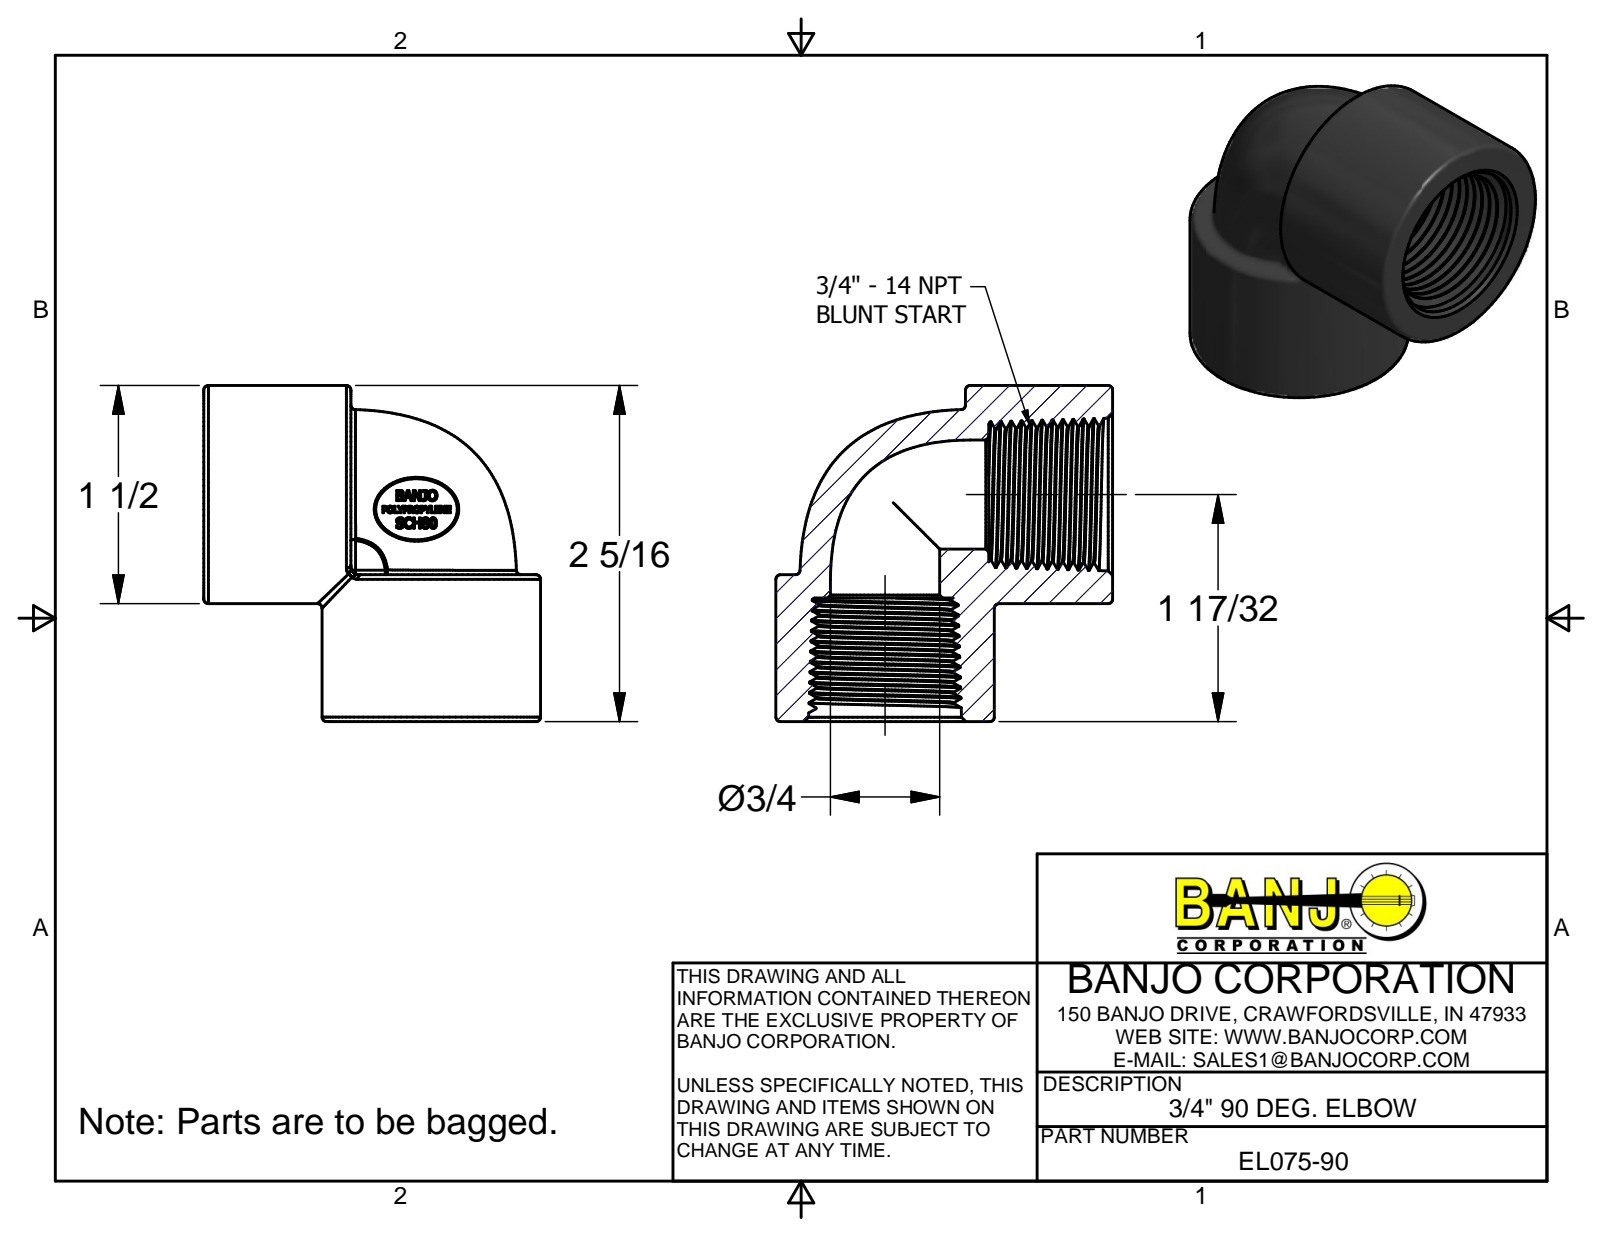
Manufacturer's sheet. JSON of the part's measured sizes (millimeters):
{"part_name": "EL075-90", "step_written_by": "Autodesk Inventor 2014 (AUTOMOTIVE_DESIGN)", "units": "millimeters", "bodies": {"solids": 2, "faces": 449, "planar": 173, "cylindrical": 11, "other": 265}, "overall_size": [58.73, 58.7, 38.1], "round_holes": [[19.05, 2]], "round_bosses_or_shafts": [[38.1, 2]], "partial_cylinders_radius": [[0.79, 4], [13.96, 1], [14.01, 1]], "face_to_face_distances": [25.65, 4.06, 21.59, 25.4, 1.01, 1.05, 2.9, 3.72, 4.51, 1.02]}
